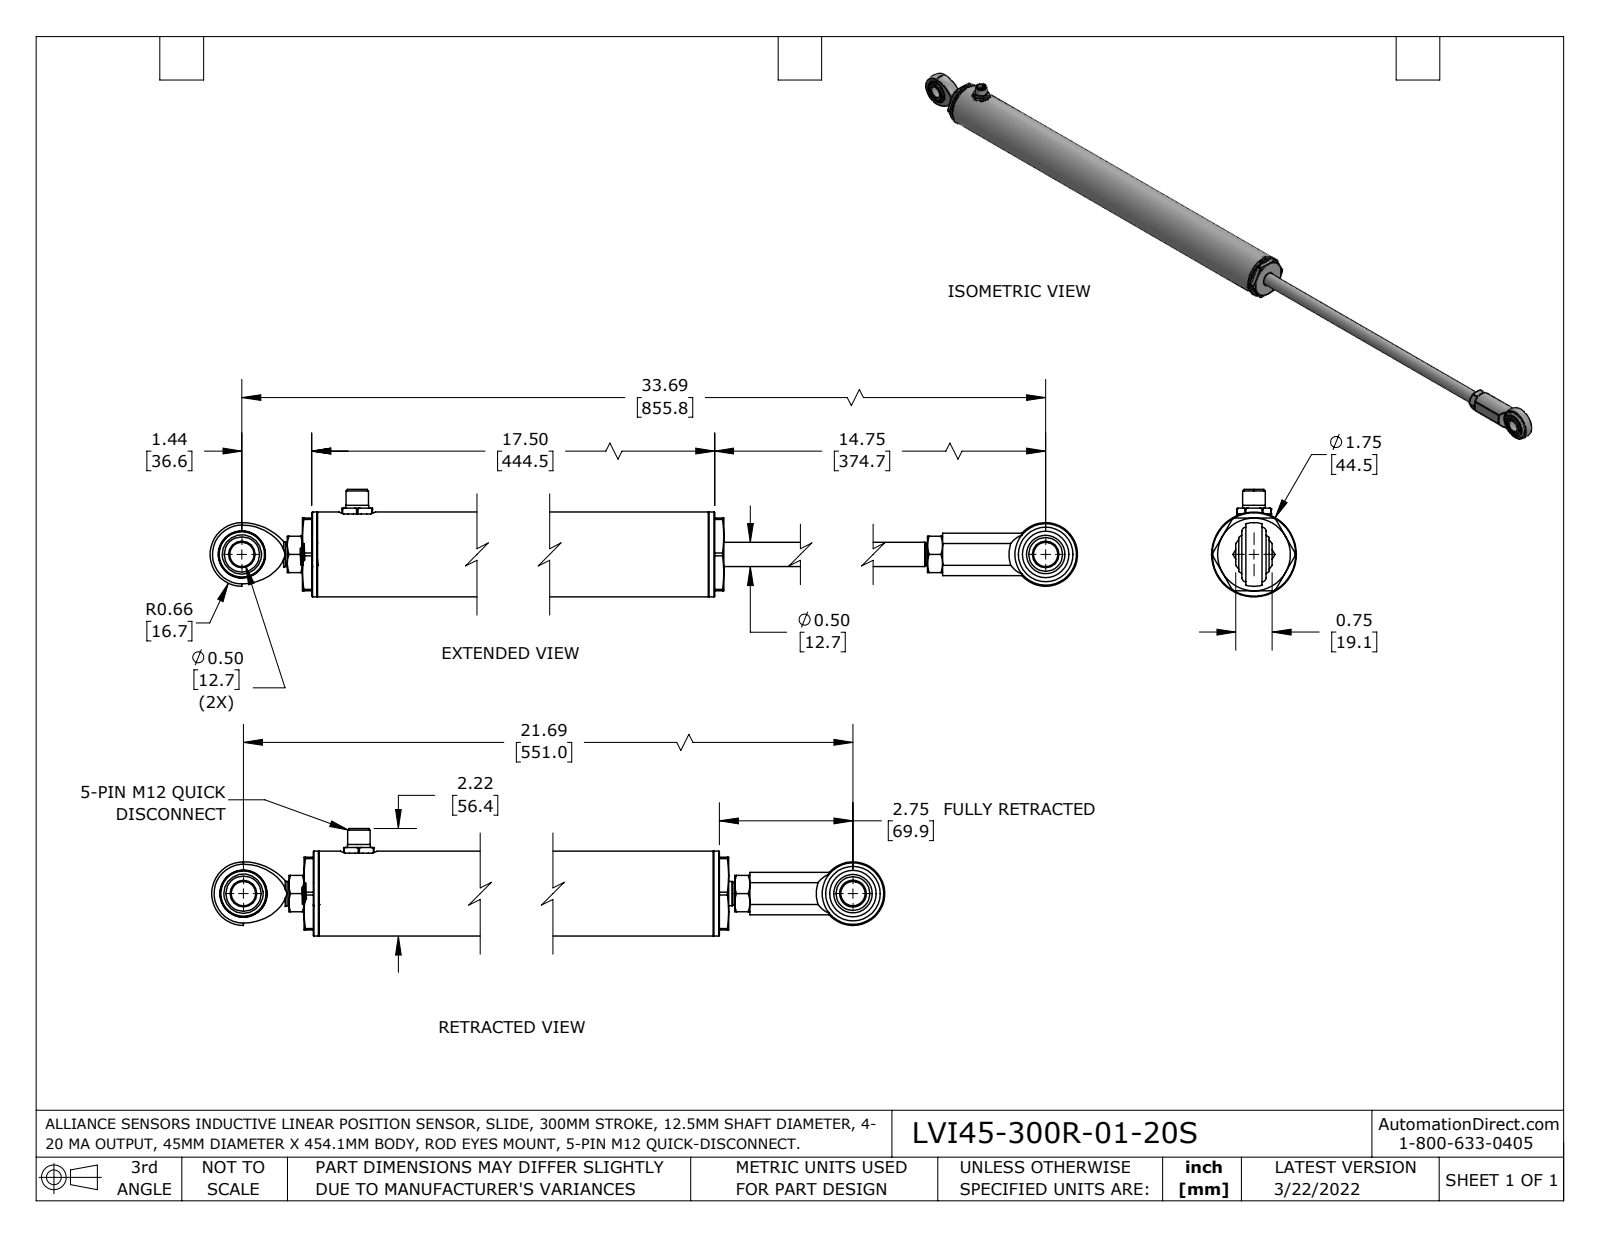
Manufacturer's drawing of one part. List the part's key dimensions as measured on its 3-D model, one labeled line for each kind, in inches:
Part name (STEP PRODUCT): 3100-0013; 3100-0016-YY; 3100-0203-XX-Y_3100-0203-12-Y; LVI45-300R-01-20S (+8 more)
STEP written by: SolidWorks 2021 (AUTOMOTIVE_DESIGN)
Units: inches
Bodies: 23 solids, 873 faces (198 planar, 297 cylindrical, 378 other)
Overall size (bounding box): 35.004 × 2.219 × 1.75
Volume: 20.52 in³ · Surface area: 310.9 in²
Round holes (diameter × count): ⌀0.501 ×3, ⌀0.197 ×1, ⌀0.25 ×1, ⌀0.264 ×1, ⌀0.309 ×1, ⌀0.329 ×1, ⌀0.339 ×1, ⌀0.413 ×1, ⌀0.417 ×1, ⌀0.453 ×1, ⌀0.478 ×1, ⌀0.5 ×1
Round bosses / shafts (diameter × count): ⌀0.031 ×5, ⌀1.75 ×1, ⌀1.625 ×1, ⌀1.562 ×1, ⌀1.531 ×1, ⌀1.5 ×1, ⌀1.47 ×1, ⌀1.384 ×1
Partial cylindrical surfaces — rounded edges, fillets, slot ends (radius × count): R0.325 ×1, R0.354 ×1, R0.378 ×1, R0.38 ×1, R0.438 ×1, R0.85 ×1
Main face-to-face distances: 1.93, 0.5, 0.38, 0.69, 2.62, 15.573, 2.24, 1.55, 15.763, 15.073
Hole centre spacings: 0.5, 33.693
